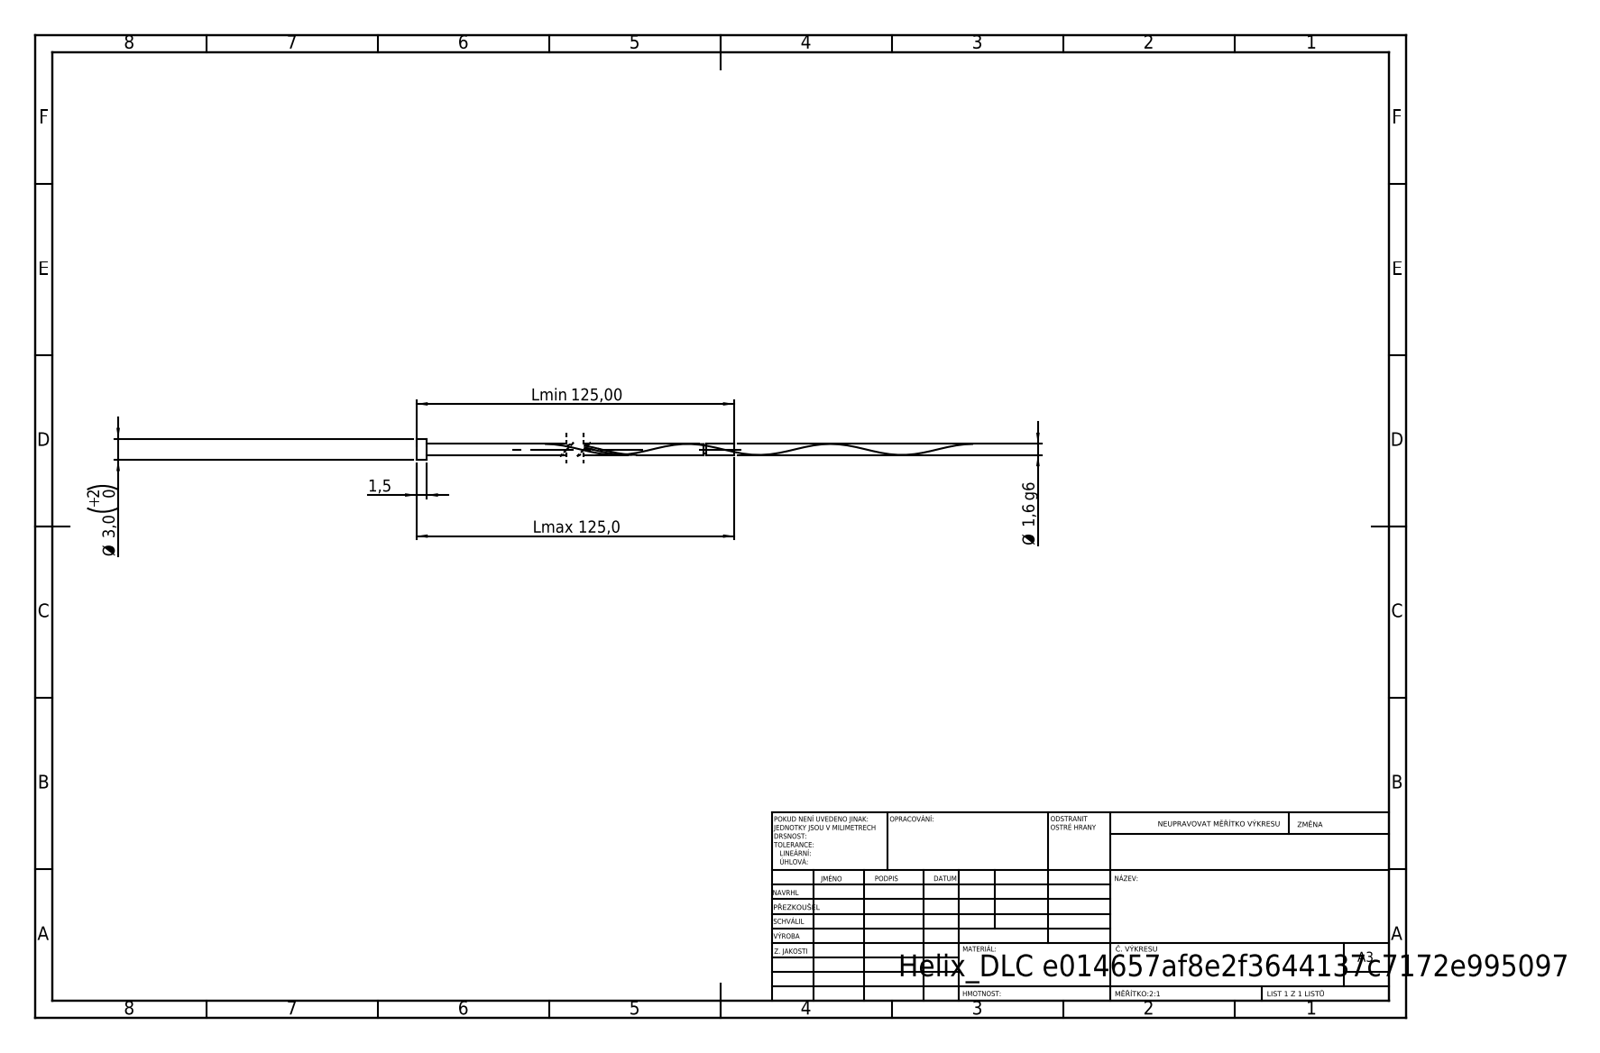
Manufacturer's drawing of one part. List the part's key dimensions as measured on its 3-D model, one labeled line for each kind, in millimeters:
STEP written by: SolidWorks 2019 (CONFIG_CONTROL_DESIGN)
Units: millimetres
Bodies: 1 solid, 16 faces (6 planar, 9 cylindrical, 1 other)
Overall size (bounding box): 125 × 3 × 3
Volume: 312 mm³ · Surface area: 870 mm²
Round bosses / shafts (diameter × count): ⌀3 ×1, ⌀1.6 ×1, ⌀1.28 ×1
Main face-to-face distances: 1.5, 125, 123.5, 120.87, 119.37, 4.13, 120.55, 119.05, 0.32, 4.45
